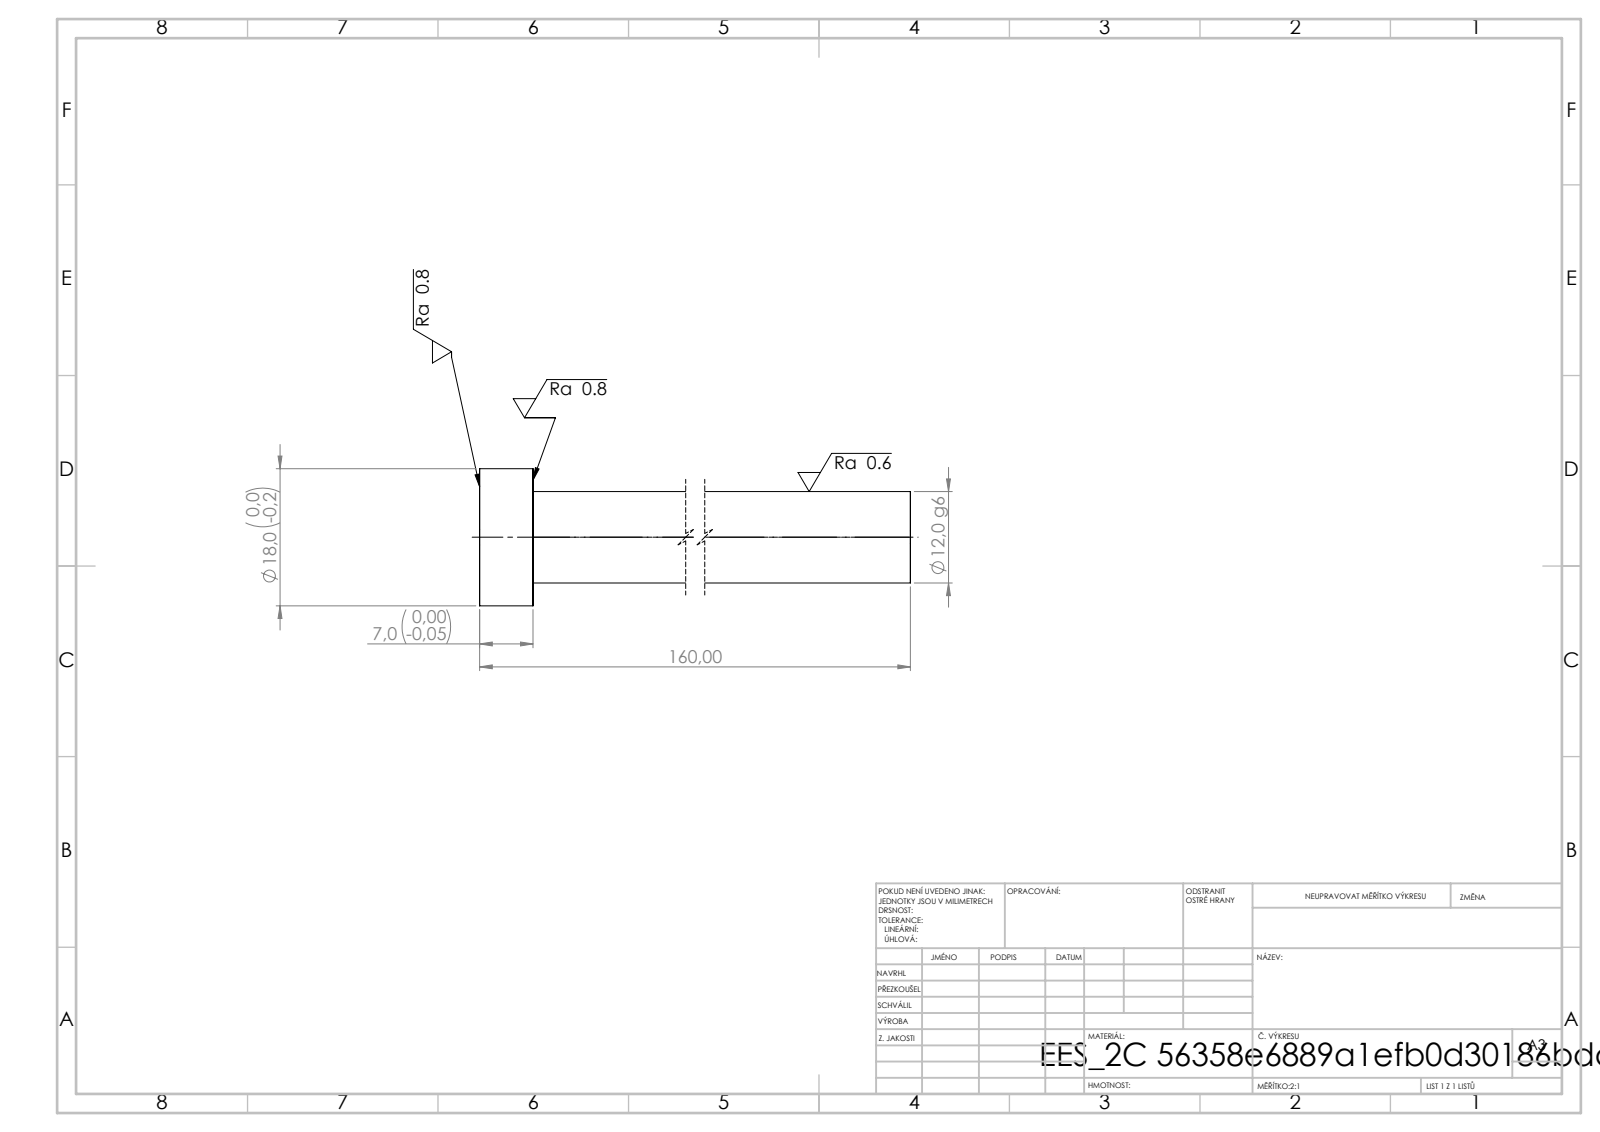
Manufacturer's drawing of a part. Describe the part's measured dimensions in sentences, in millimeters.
Its 3-D file was written by "SolidWorks 2019 (CONFIG_CONTROL_DESIGN)". It is 1 solid with 7 faces: 3 planar, 4 cylindrical and 0 other. Overall it measures 160 by 18 by 18 millimeters. Its volume is 19 085 cubic millimeters and its surface area 6 673 square millimeters. Round bosses or shafts: 1 of diameter 18, 1 of diameter 12. The main face-to-face distances are 7, 160, 153.
